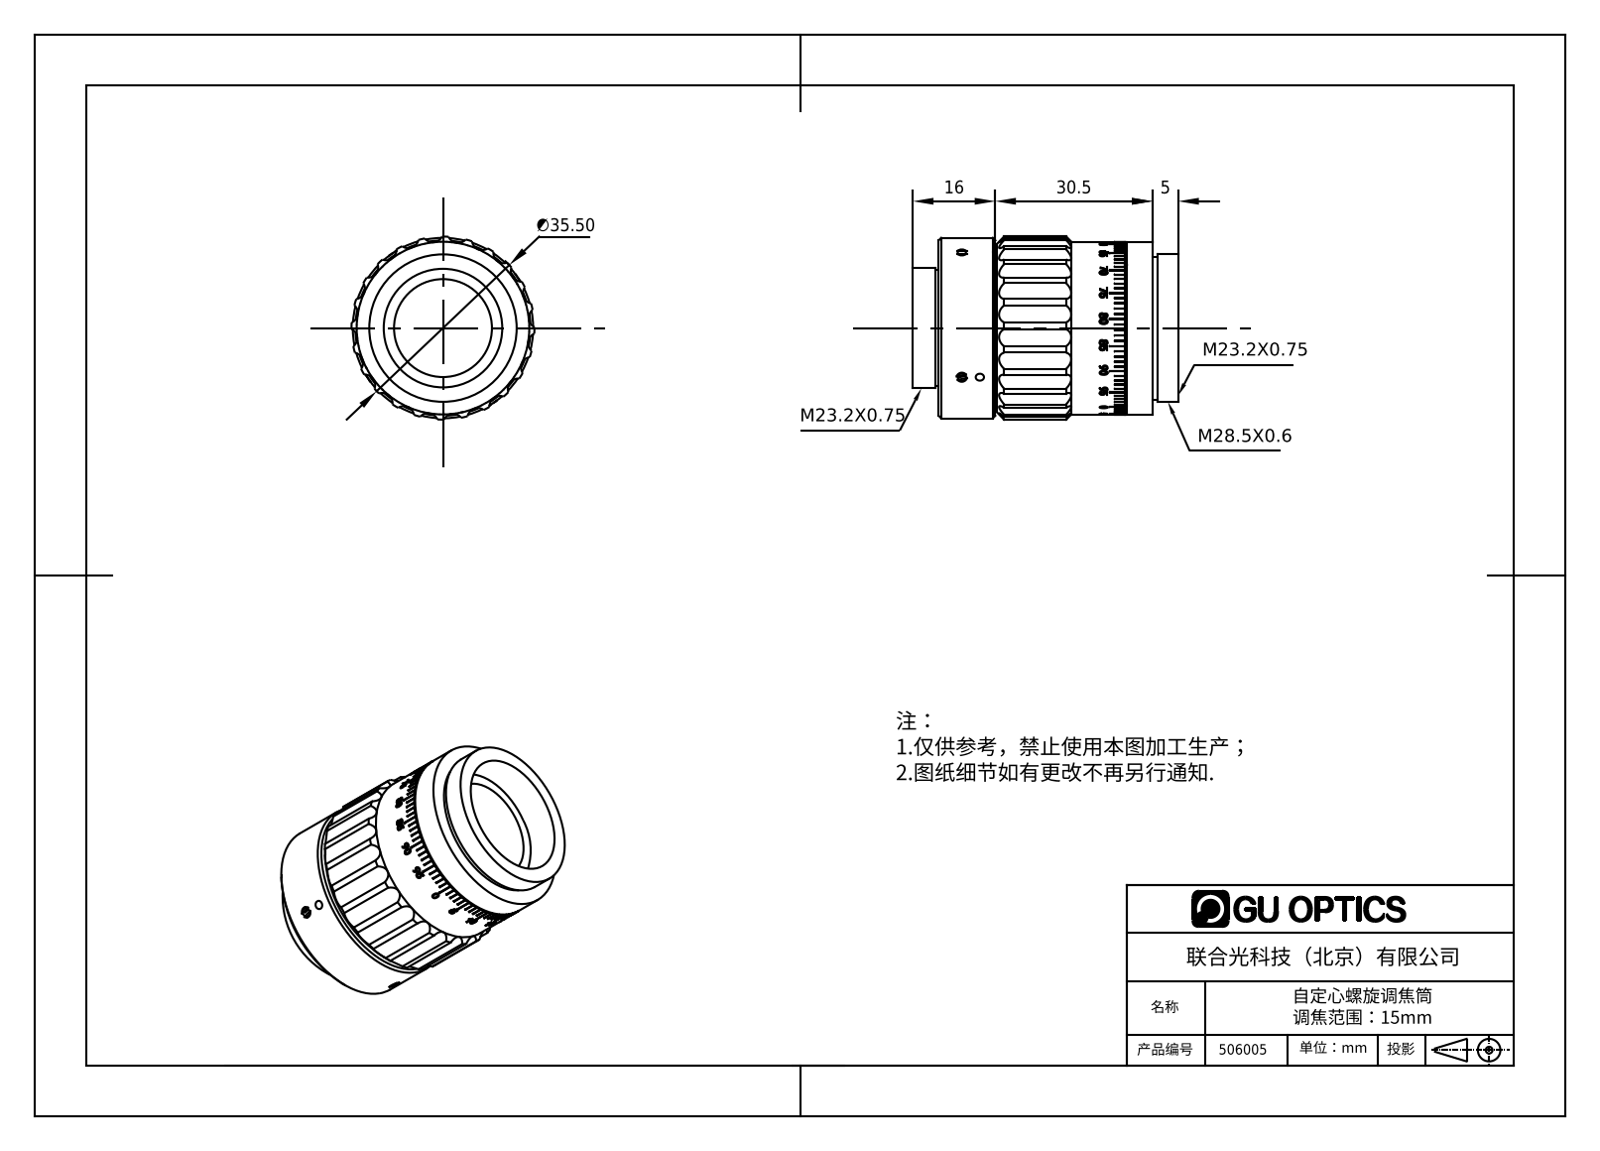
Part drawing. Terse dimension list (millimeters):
name: HFA19-01连动圈; HFA19-02定位筒; M23.2锁紧环; 限位铜钉 (+2 more)
written by: SolidWorks 2016 (AUTOMOTIVE_DESIGN)
unit: mm
bodies: 8 solids, 1555 faces (658 planar, 347 cylindrical, 550 other)
size: 51.5 × 35.5 × 35.5
volume: 26 628 mm³; area: 24 446 mm²
holes: 5× ⌀1.6, 2× ⌀2.1, 1× ⌀19, 1× ⌀23, 1× ⌀25, 1× ⌀25.5, 1× ⌀25.7, 1× ⌀28.7, 1× ⌀31, 1× ⌀32
bosses: 4× ⌀2.06, 4× ⌀2, 1× ⌀35, 1× ⌀33.5, 1× ⌀31.6, 1× ⌀30.5, 1× ⌀30, 1× ⌀28.6
rounds: 24× R2, 4× R12.75, 2× R12.5, 1× R14.9, 1× R16.73, 1× R17.75
face distances: 2, 5, 12, 14, 1, 29.27, 41.5, 12.23, 10, 34.5
hole spacings: 3.5
